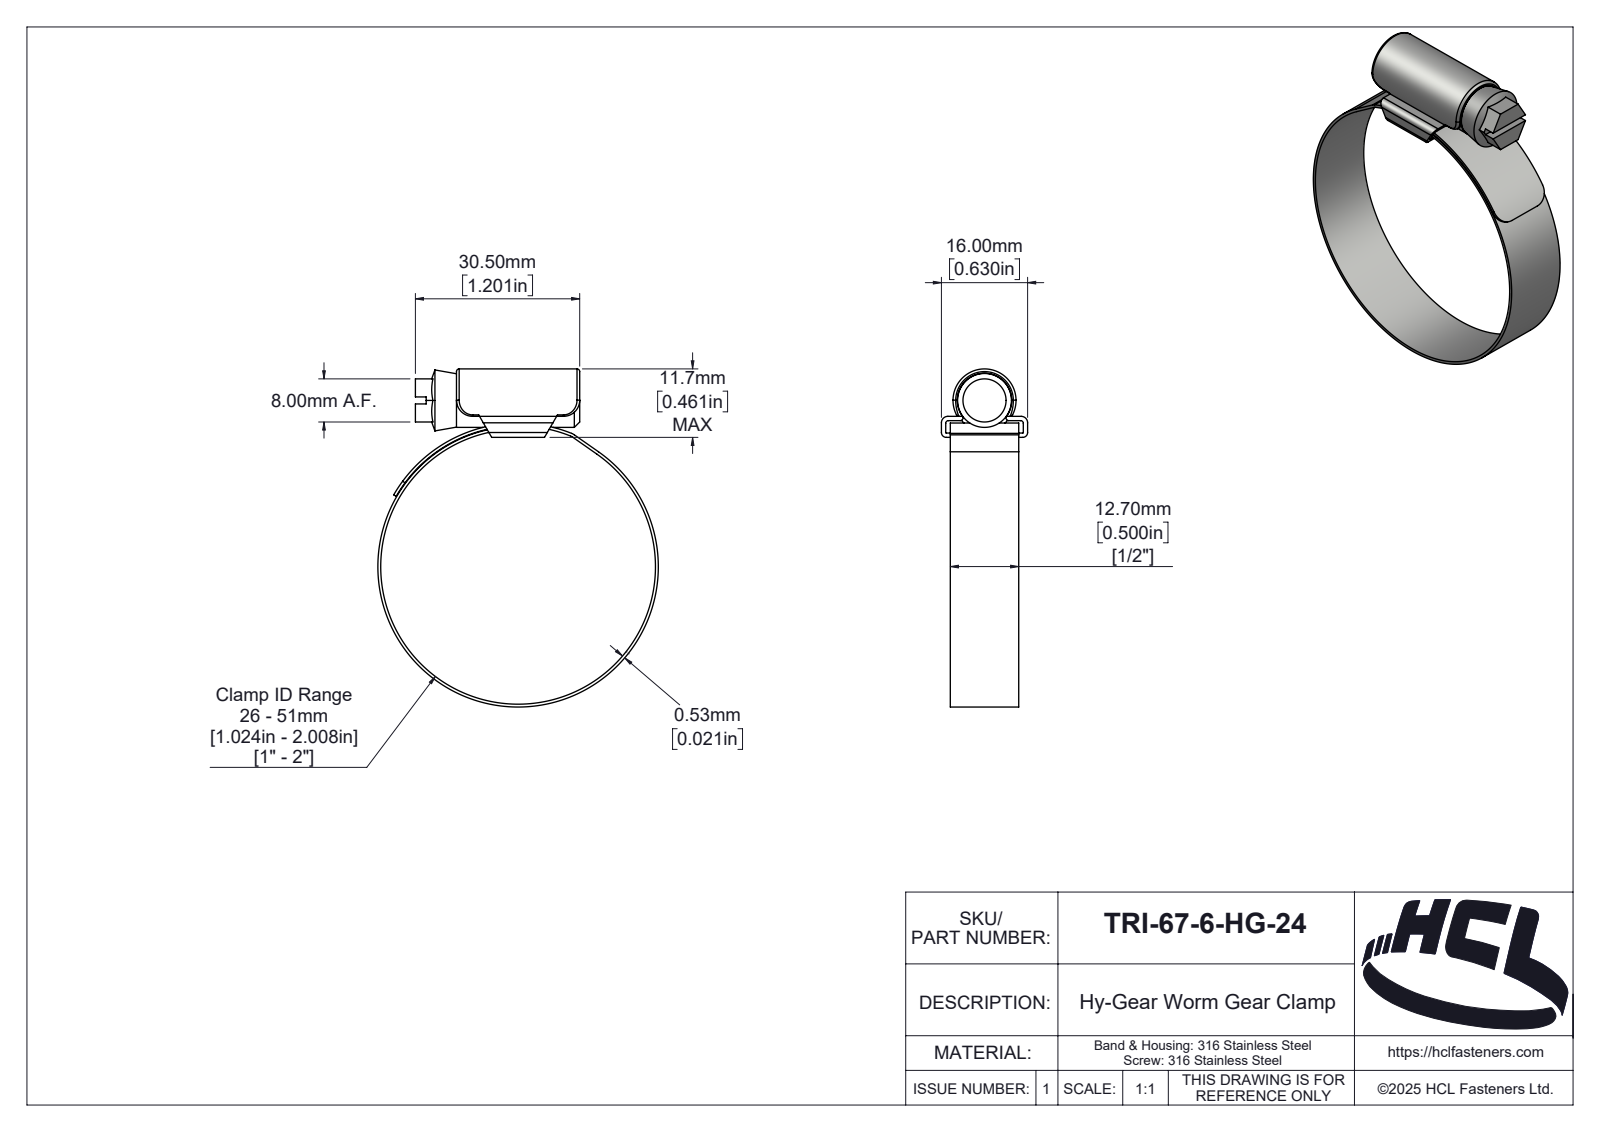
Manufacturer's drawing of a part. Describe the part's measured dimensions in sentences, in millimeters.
The part is named "TRI-57-0-HG-24". Its 3-D file was written by "SolidWorks 2025 (AUTOMOTIVE_DESIGN)". It is 3 solids with 189 faces: 39 planar, 89 cylindrical and 61 other. Overall it measures 62.73 by 52.06 by 16 millimeters. Its volume is 4 269 cubic millimeters and its surface area 7 927 square millimeters. Round holes: 1 of diameter 51. Round bosses or shafts: 1 of diameter 52.06, 1 of diameter 10. Partial cylindrical surfaces (rounded edges, fillets, slot ends): 6 of radius 0.5, 4 of radius 3, 2 of radius 0.1, 2 of radius 0.9, 2 of radius 1.2, 1 of radius 0.46, 1 of radius 1.89, 1 of radius 2. The main face-to-face distances are 0.8, 3.1, 12.7, 2.3, 0.53, 3.9, 30.5, 1.65, 14.35, 15.2.
